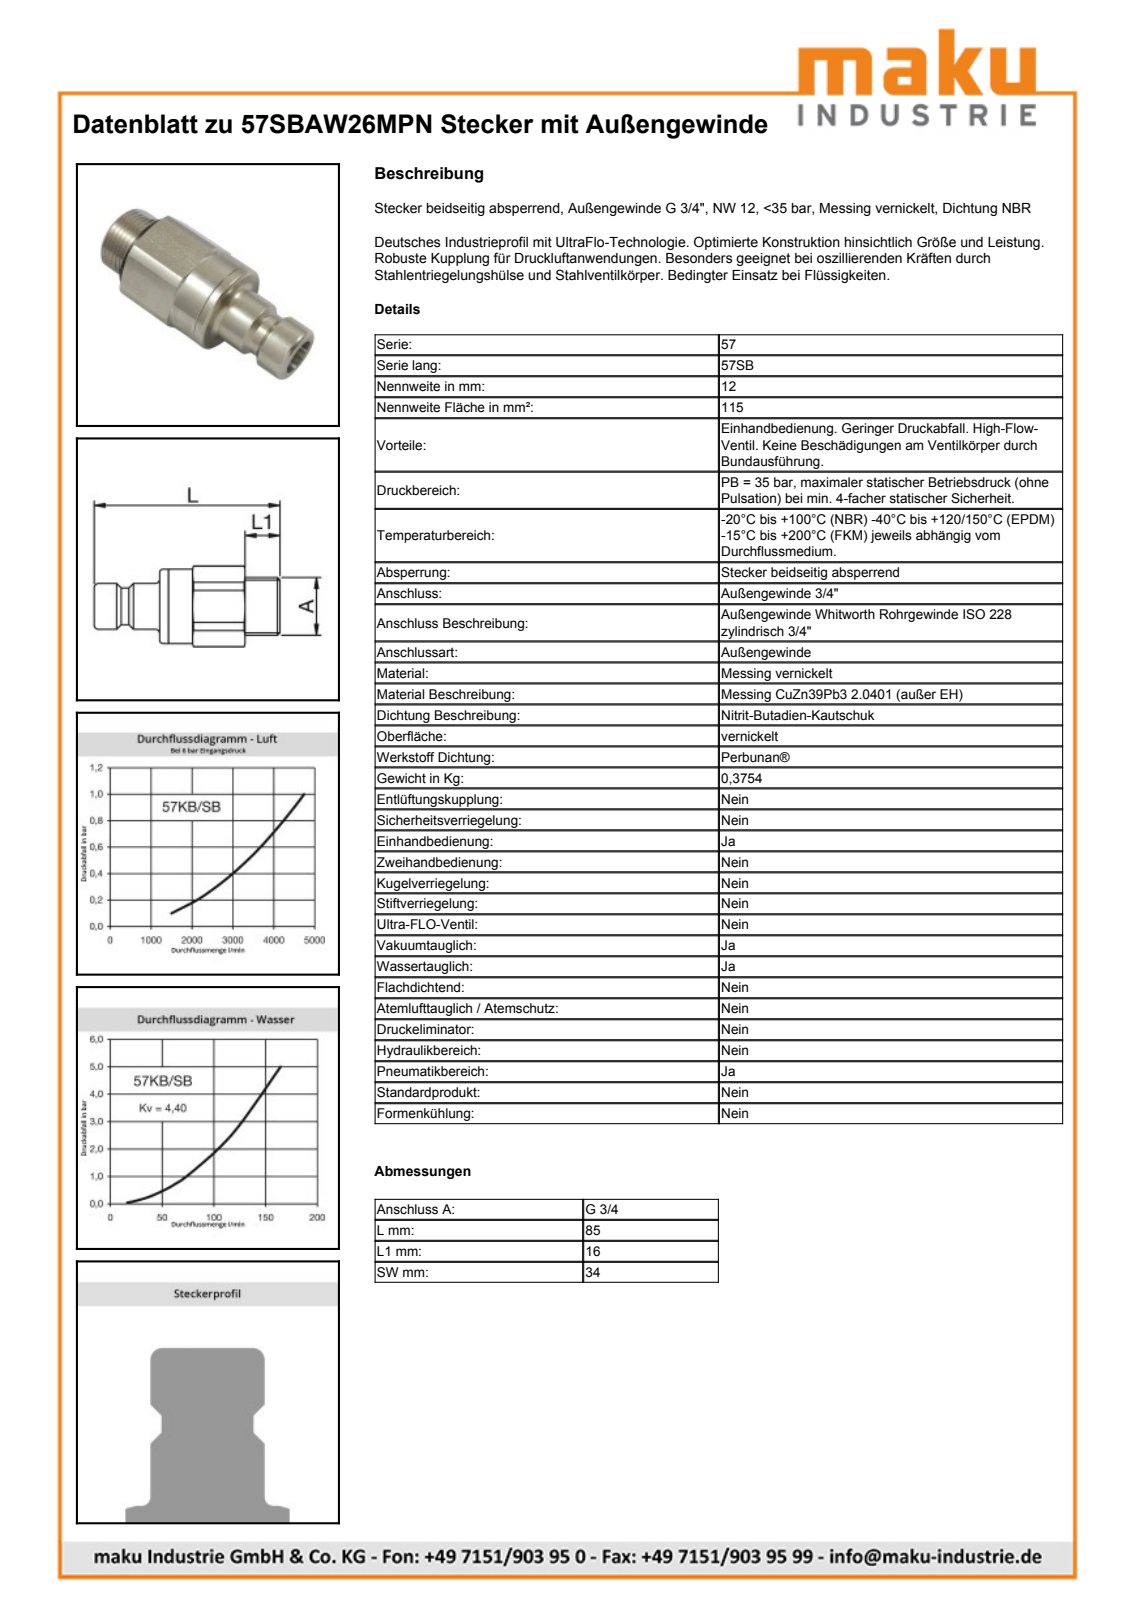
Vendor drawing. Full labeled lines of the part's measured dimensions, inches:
Part name (STEP PRODUCT): D107539
STEP written by: Autodesk Inventor 2013 (AUTOMOTIVE_DESIGN)
Units: inches
Bodies: 1 solid, 39 faces (10 planar, 11 cylindrical, 18 other)
Overall size (bounding box): 3.346 × 1.457 × 1.402
Volume: 3.391 in³ · Surface area: 14.5 in²
Round bosses / shafts (diameter × count): ⌀1.339 ×1, ⌀1.041 ×1, ⌀0.823 ×1, ⌀0.661 ×1
Partial cylindrical surfaces — rounded edges, fillets, slot ends (radius × count): R0.728 ×1
Main face-to-face distances: 1.339, 0.63, 1.338, 1.535, 2.165, 1.181, 2.717, 3.346
